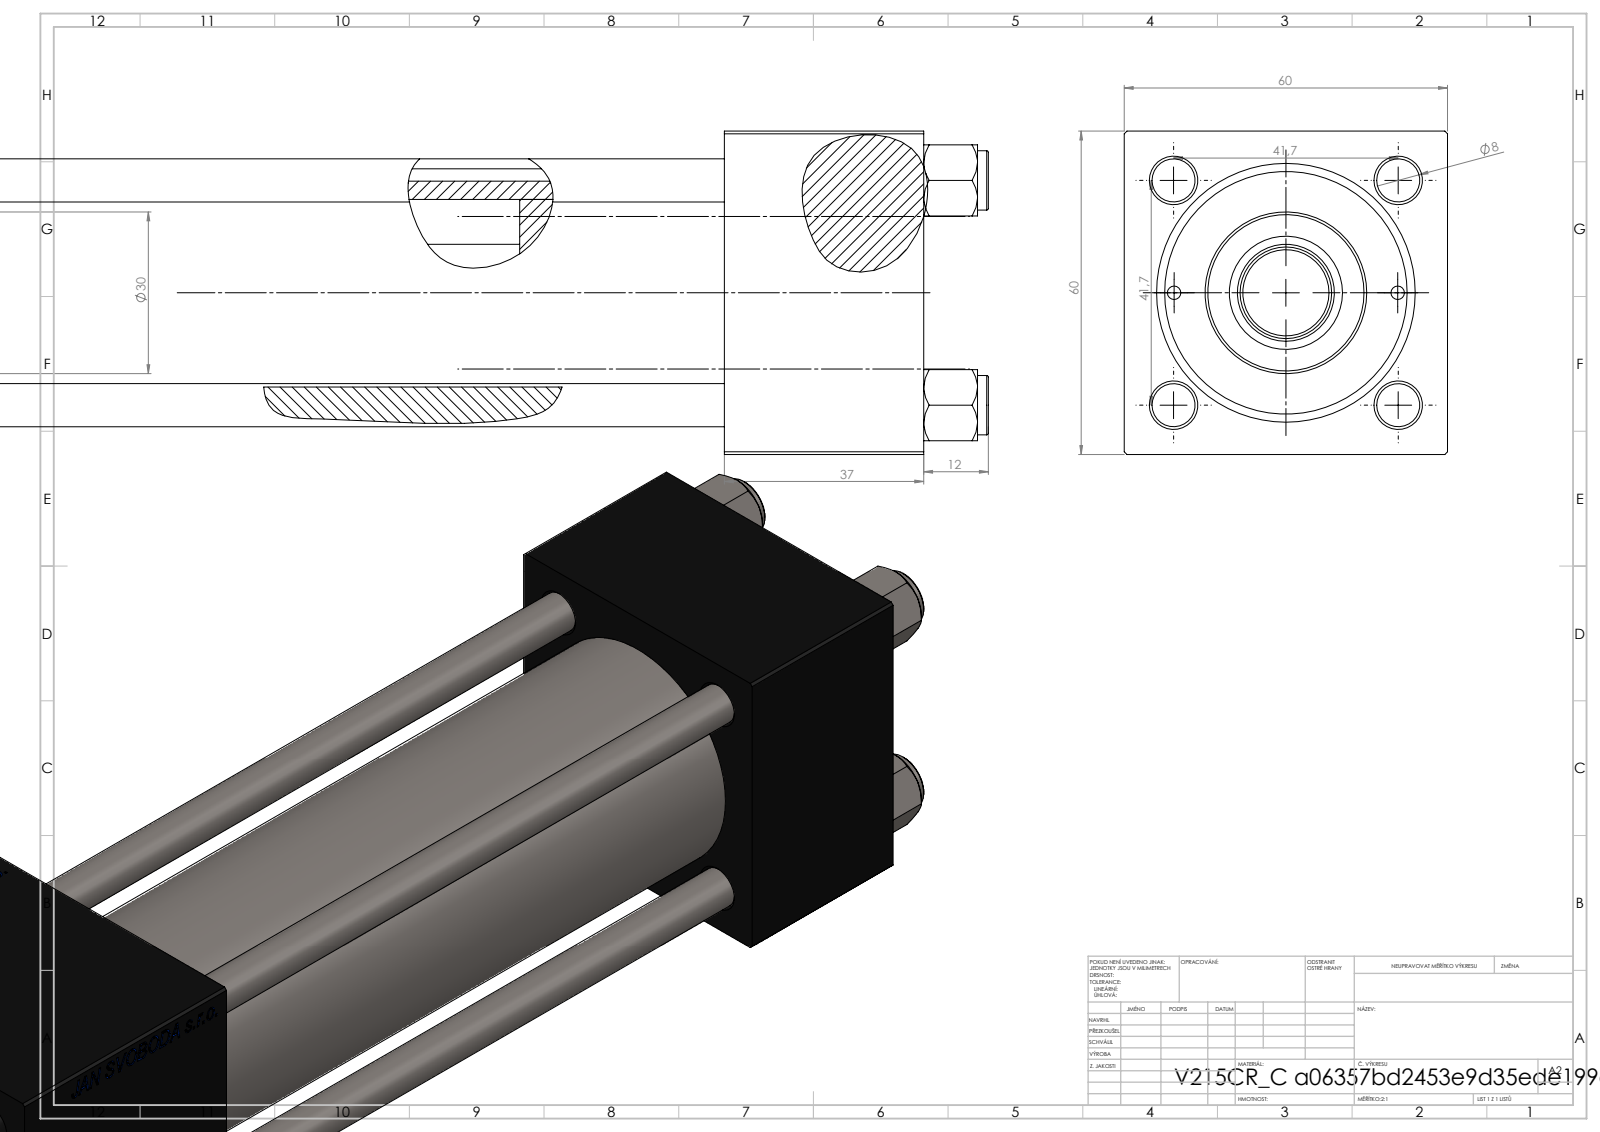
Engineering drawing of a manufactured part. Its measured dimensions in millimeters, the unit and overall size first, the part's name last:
Units: millimetres
Overall size (bounding box): 285 × 60 × 60
Round holes (diameter × count): ⌀8 ×4, ⌀2.5 ×2, ⌀7 ×2, ⌀16.66 ×2, ⌀24 ×2, ⌀8.5 ×1, ⌀18 ×1, ⌀21 ×1, ⌀31 ×1, ⌀40 ×1, ⌀45 ×1
Round bosses / shafts (diameter × count): ⌀11 ×5, ⌀46 ×1, ⌀30 ×1, ⌀17 ×1
Main face-to-face distances: 60, 37, 228, 191, 53, 175, 138, 199.3, 162.3, 24.3
Hole centre spacings: 20.85, 29.49, 41.7, 46.53, 20.75, 58.97, 41.5, 172.5
Volume: 474 598 mm³ · Surface area: 140 899 mm²
Bodies: 12 solids, 1165 faces (531 planar, 94 cylindrical, 540 other)
Part name (STEP PRODUCT): V215CR_VCP_C; V215CR_C_Body; NUT_M5_C; V215_VC_A (+2 more)
STEP written by: SolidWorks 2019 (CONFIG_CONTROL_DESIGN)
